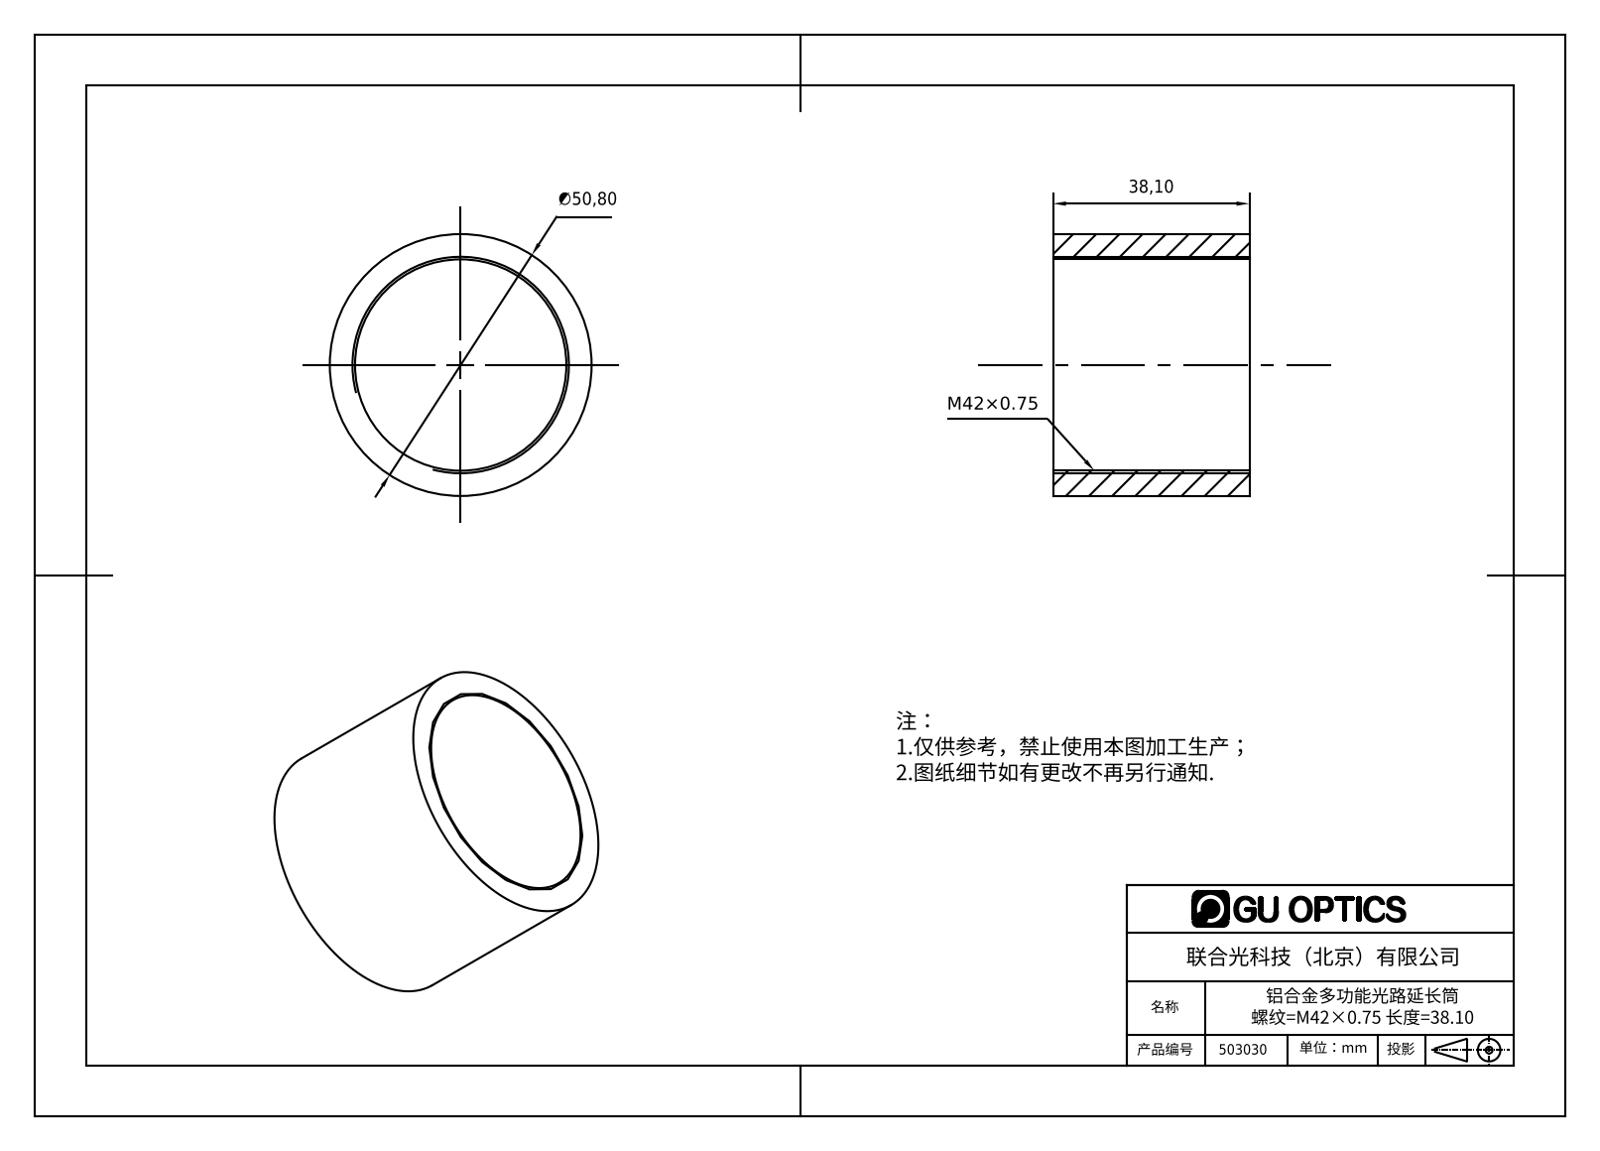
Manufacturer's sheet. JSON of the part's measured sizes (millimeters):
{"part_name": "503030", "step_written_by": "SolidWorks 2016 (AUTOMOTIVE_DESIGN)", "units": "millimeters", "bodies": {"solids": 1, "faces": 6, "planar": 2, "cylindrical": 4, "other": 0}, "overall_size": [50.8, 50.8, 38.1], "volume_mm3": 26921, "surface_area_mm2": 12401, "round_holes": [[41, 1]], "round_bosses_or_shafts": [[50.8, 1]], "face_to_face_distances": [38.1]}
